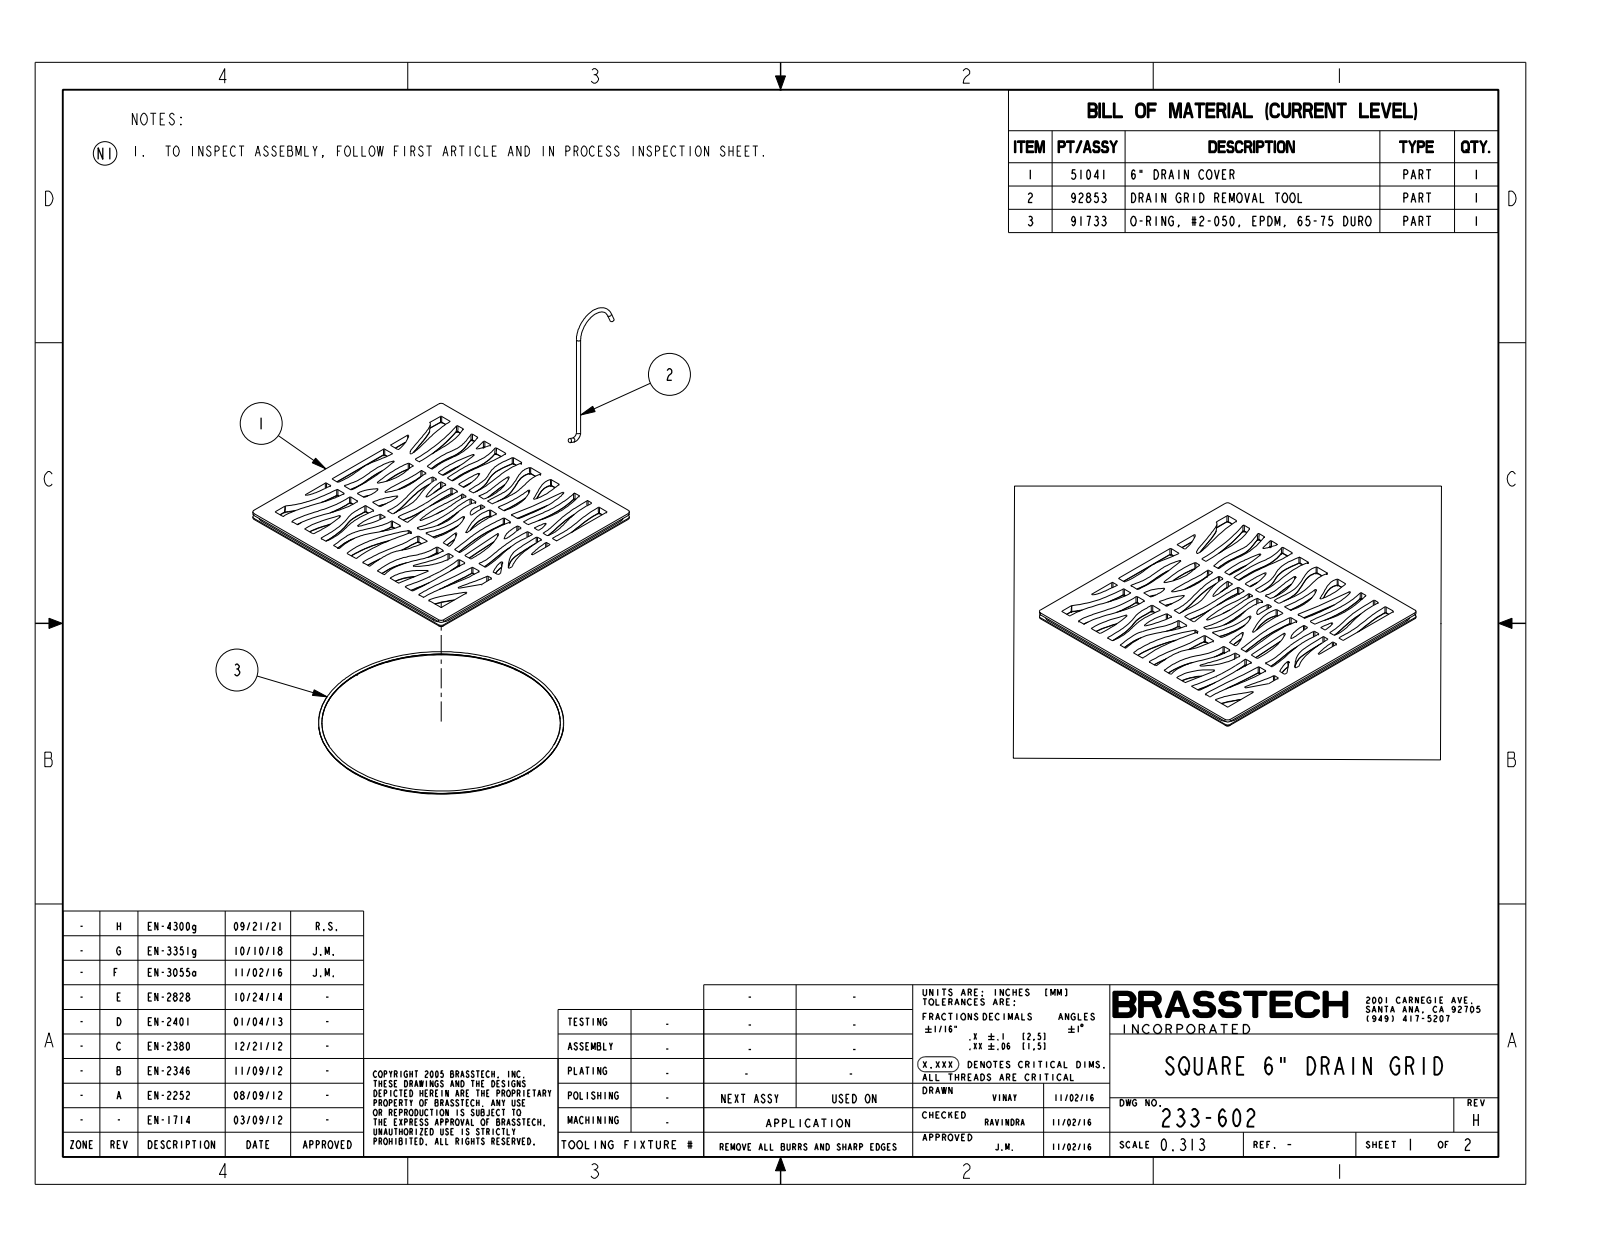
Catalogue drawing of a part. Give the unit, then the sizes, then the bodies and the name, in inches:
Units: inches
Overall size (bounding box): 5.895 × 5.895 × 0.188
Partial cylindrical surfaces — rounded edges, fillets, slot ends (radius × count): R0.02 ×37, R0.08 ×4, R0.25 ×4
Main face-to-face distances: 0.188, 0.042, 5.854, 0.134, 0.054, 0.054, 0.08, 0.134, 5.895, 5.812
Volume: 4.05 in³ · Surface area: 77.44 in²
Bodies: 1 solid, 820 faces (112 planar, 118 cylindrical, 590 other)
Part name (STEP PRODUCT): 51041
STEP written by: CREO PARAMETRIC BY PTC INC, 2018400 (AUTOMOTIVE_DESIGN)
